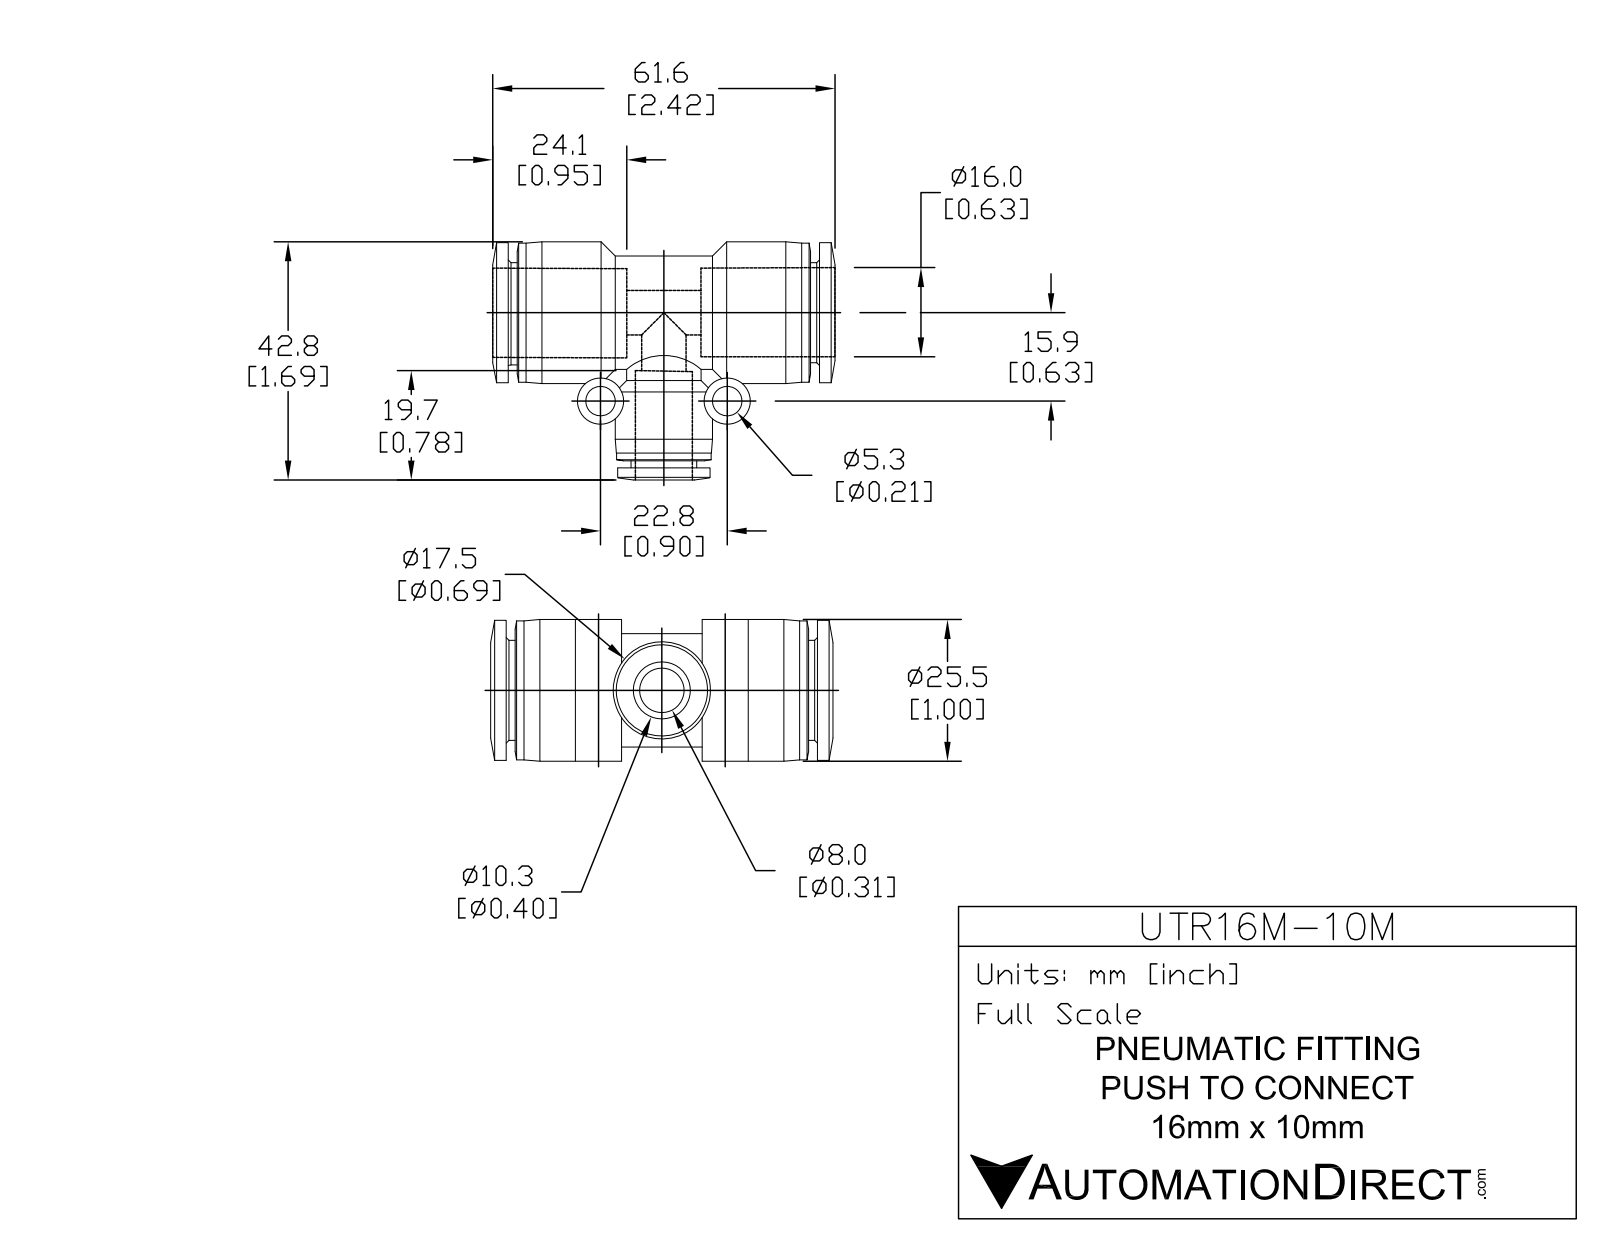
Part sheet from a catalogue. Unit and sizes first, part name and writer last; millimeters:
Units: millimetres
Overall size (bounding box): 61.6 × 42.8 × 25.5
Round holes (diameter × count): ⌀5.3 ×2, ⌀8 ×2, ⌀10 ×1, ⌀16 ×1
Round bosses / shafts (diameter × count): ⌀8.3 ×2, ⌀25.5 ×1, ⌀24.74 ×1, ⌀20.4 ×1, ⌀20 ×1, ⌀17.5 ×1, ⌀16.8 ×1, ⌀13.93 ×1
Main face-to-face distances: 1, 57.6, 22.6, 36, 21.6, 35, 58.6, 56.6, 13.4, 0.8
Hole centre spacings: 22.8
Volume: 20 806 mm³ · Surface area: 12 989 mm²
Bodies: 1 solid, 89 faces (19 planar, 49 cylindrical, 21 other)
Part name (STEP PRODUCT): UTR16M-10M
STEP written by: SolidWorks 2015 (CONFIG_CONTROL_DESIGN)
